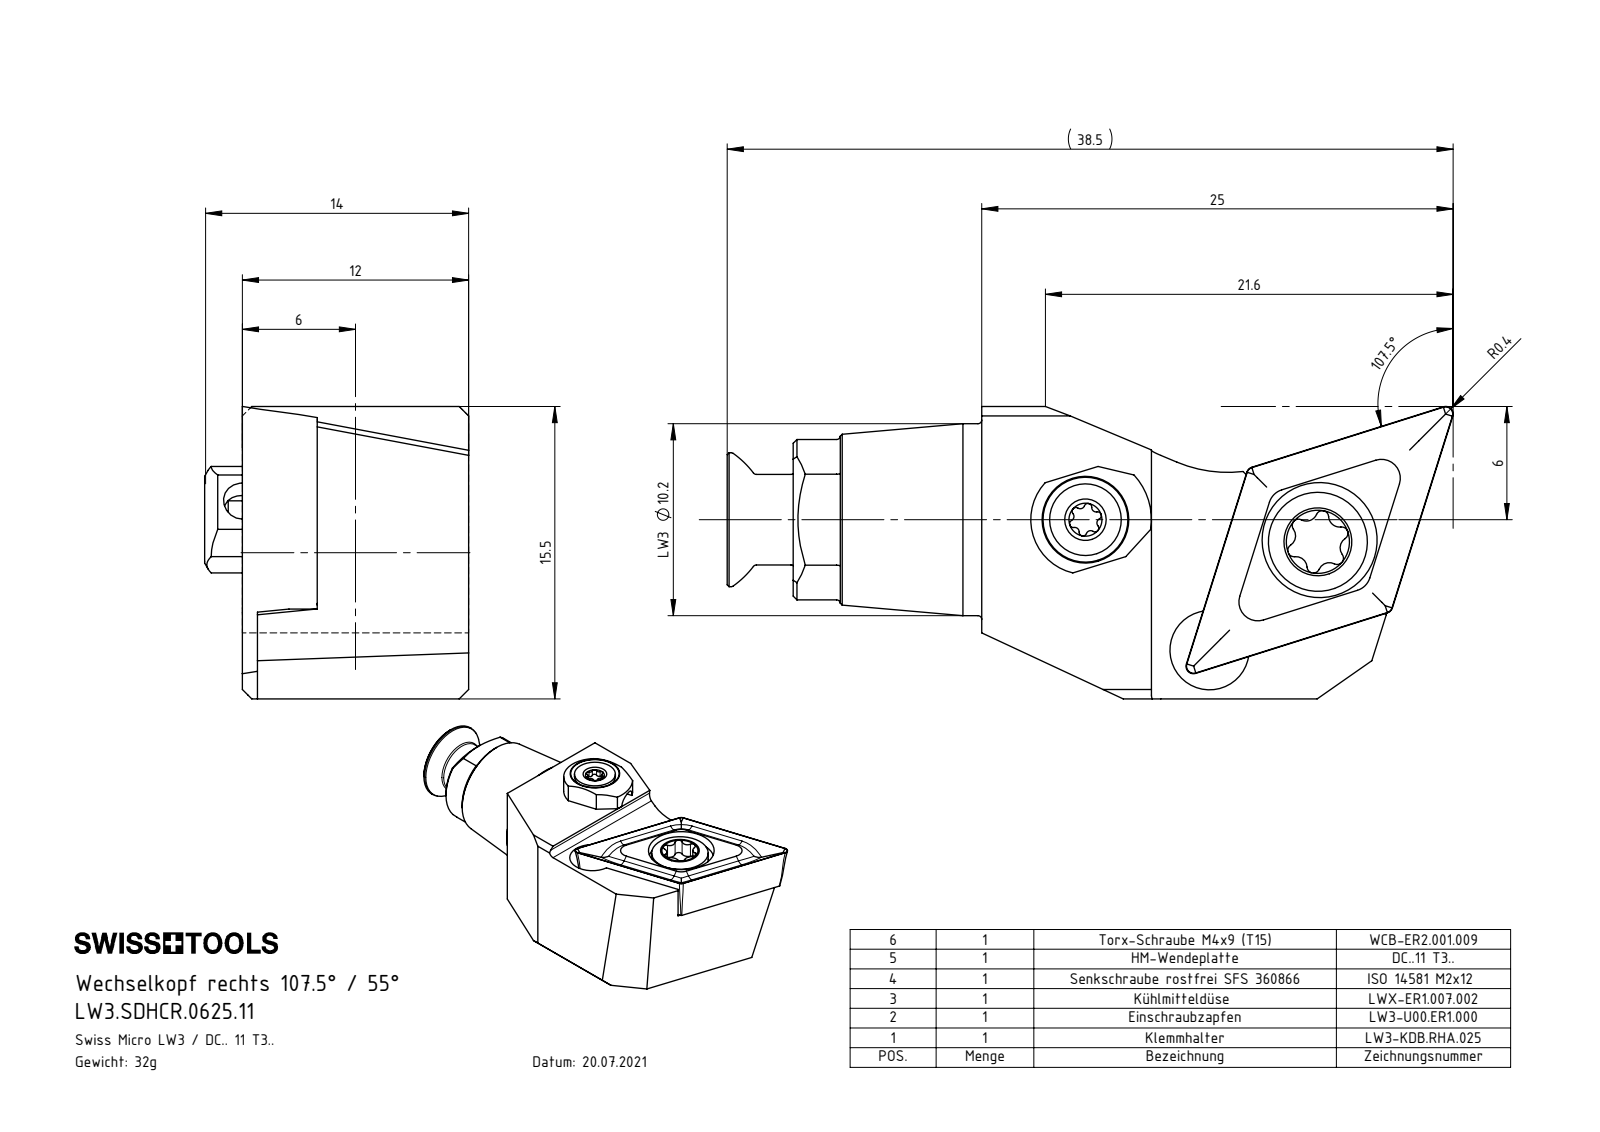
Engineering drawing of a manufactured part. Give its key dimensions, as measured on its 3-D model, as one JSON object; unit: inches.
{"part_name": "ISO 14581 - M2x12; LW3.SDHCR.0625.11; LW3-U00.ER1.000_B; LWX-ER1.007.002 (+3 more)", "step_written_by": "SolidWorks 2022 (CONFIG_CONTROL_DESIGN)", "units": "inches", "bodies": {"solids": 6, "faces": 255, "planar": 71, "cylindrical": 79, "other": 105}, "overall_size": [1.512, 0.61, 0.551], "volume_in3": 0.231, "surface_area_in2": 4.697, "round_holes": [[0.063, 1], [0.079, 1], [0.098, 1], [0.118, 1], [0.13, 1], [0.165, 1], [0.173, 1], [0.217, 1], [0.24, 1]], "round_bosses_or_shafts": [[0.401, 1], [0.272, 1], [0.236, 1], [0.207, 1], [0.197, 1], [0.189, 1], [0.157, 1], [0.15, 1]], "partial_cylinders_radius": [[0.008, 8], [0.009, 6], [0.013, 6], [0.023, 6], [0.02, 1], [0.039, 1], [0.114, 1], [0.138, 1]], "face_to_face_distances": [0.472, 0.316, 0.156, 0.441, 0.125, 0.031, 0.079, 0.098, 0.528, 0.61], "hole_center_spacings": [0.32, 0.325, 0.376, 0.488, 0.491]}
